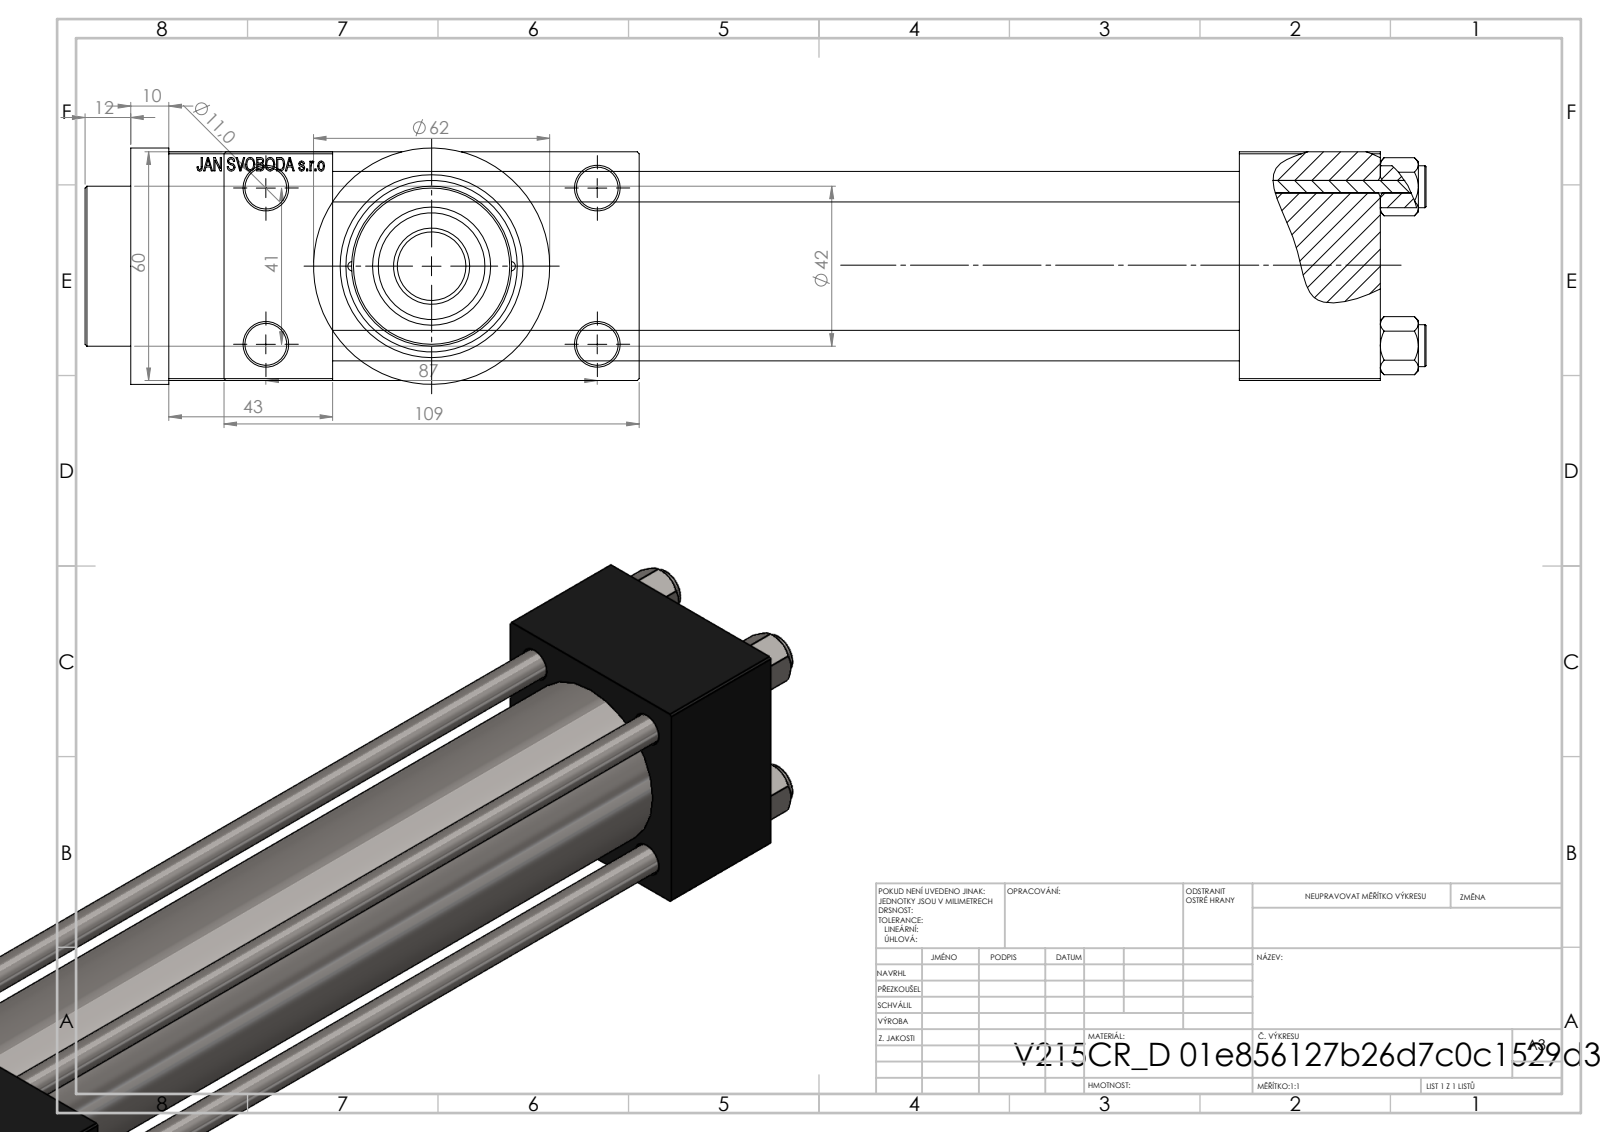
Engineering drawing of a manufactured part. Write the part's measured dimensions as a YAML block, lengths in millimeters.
part_name: "NUT_M5_D; FEMALE_PART_FOR_DFA; V215_VC_A; MFA (+3 more)"
step_written_by: "SolidWorks 2019 (CONFIG_CONTROL_DESIGN)"
units: millimeters
bodies: {solids: 13, faces: 1201, planar: 532, cylindrical: 105, other: 564}
overall_size: [352, 109, 62]
volume: 667426
surface_area: 206712
round_holes:
  - {diameter: 8, count: 4}
  - {diameter: 11, count: 4}
  - {diameter: 2.5, count: 2}
  - {diameter: 7, count: 2}
  - {diameter: 16.66, count: 2}
  - {diameter: 24, count: 2}
  - {diameter: 18.5, count: 1}
  - {diameter: 28, count: 1}
  - {diameter: 31, count: 1}
  - {diameter: 40, count: 1}
  - {diameter: 45, count: 1}
round_bosses_or_shafts:
  - {diameter: 11, count: 4}
  - {diameter: 62, count: 1}
  - {diameter: 46, count: 1}
  - {diameter: 42, count: 1}
  - {diameter: 36, count: 1}
  - {diameter: 30, count: 1}
  - {diameter: 22, count: 1}
  - {diameter: 20, count: 1}
partial_cylinders:
  - {radius: 7.5, count: 1}
  - {radius: 12, count: 1}
  - {radius: 13.5, count: 1}
face_to_face_distances: [60, 238, 24.5, 84.5, 37, 275, 43, 318, 281, 10]
hole_center_spacings: [20.85, 22.65, 29.49, 30.62, 41.7, 46.53, 47.15, 48.09]
